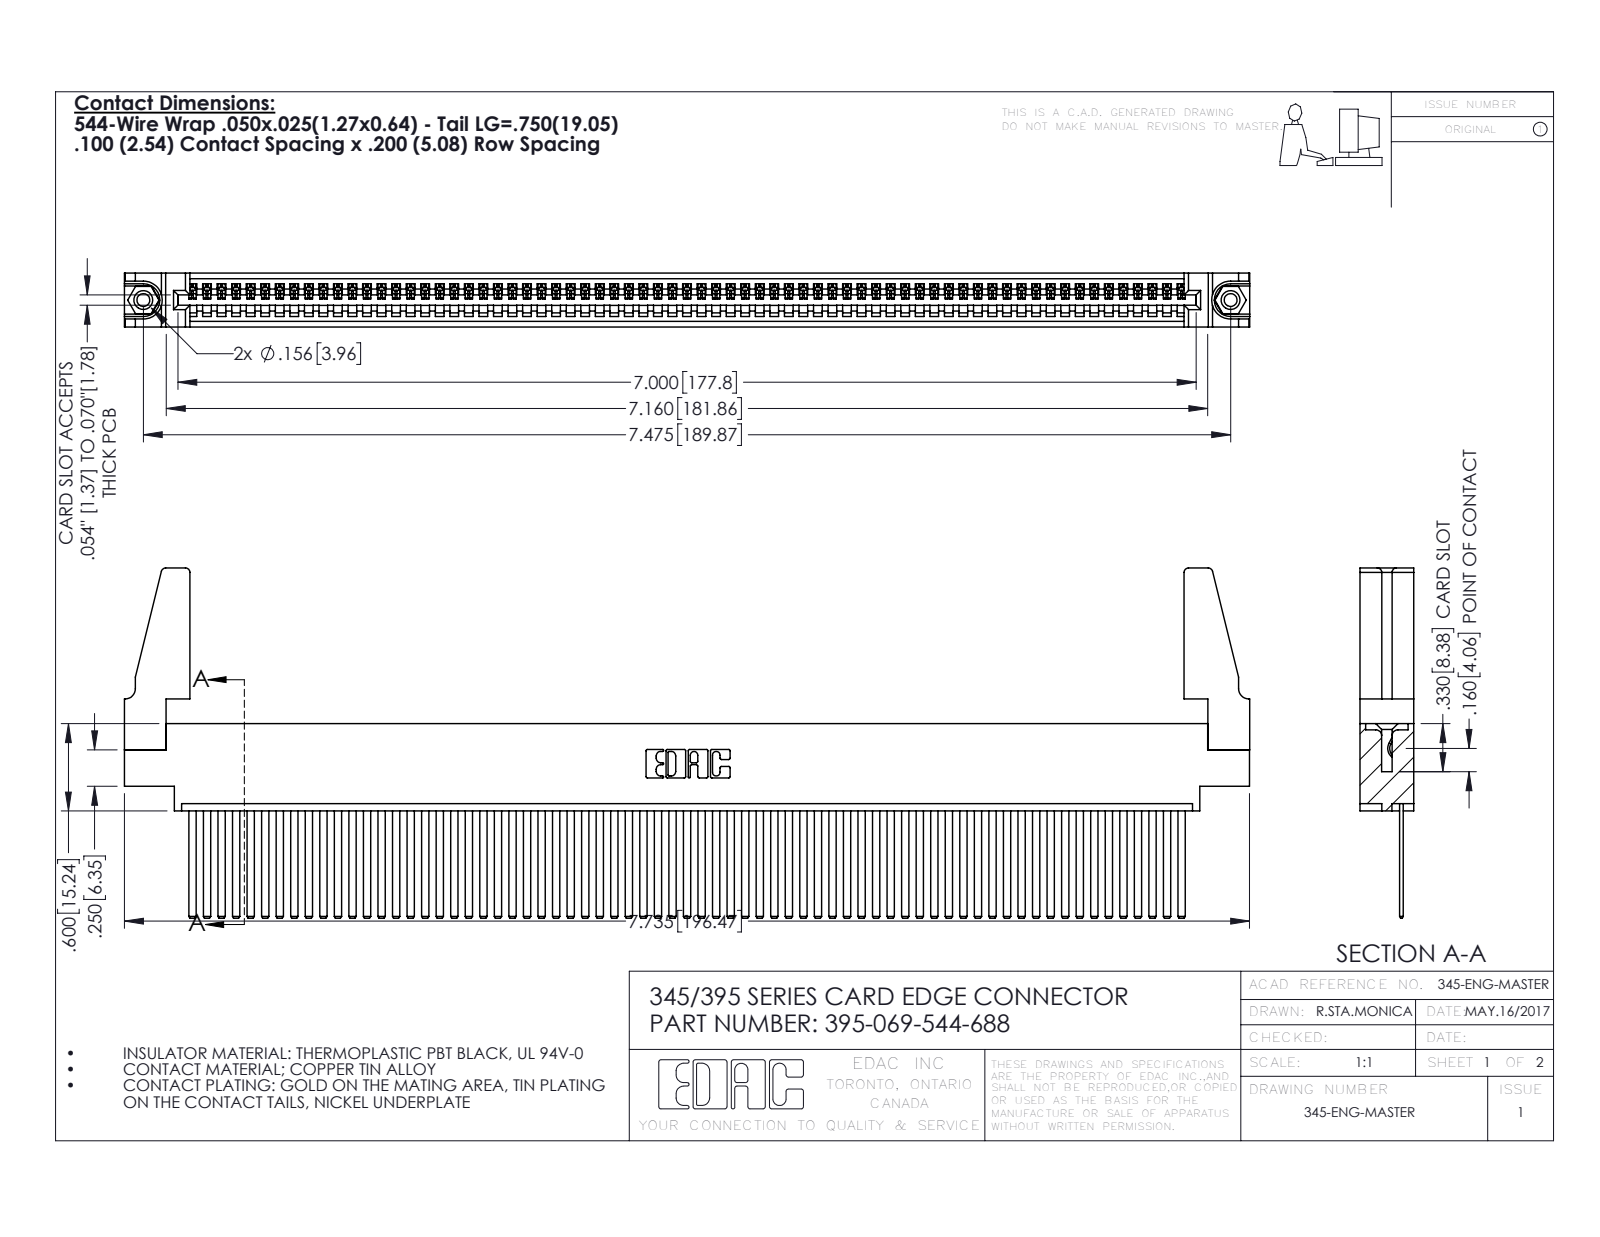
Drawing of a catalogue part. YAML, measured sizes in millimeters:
part_name: "345-250-001_345-250-001-102; 345-292-001_345-293-144; 395-069-544-688; 345-220-078_345-220-088 (+1 more)"
step_written_by: "SolidWorks 2016 (CONFIG_CONTROL_DESIGN)"
units: millimeters
bodies: {solids: 74, faces: 3842, planar: 2640, cylindrical: 1186, other: 16}
overall_size: [196.5, 61.1, 9.4]
volume: 22830
surface_area: 32030
round_holes:
  - {diameter: 2.3, count: 2}
  - {diameter: 3.2, count: 2}
  - {diameter: 4, count: 2}
  - {diameter: 1.6, count: 1}
round_bosses_or_shafts:
  - {diameter: 3.9, count: 2}
partial_cylinders:
  - {radius: 0.2, count: 138}
  - {radius: 0.3, count: 22}
  - {radius: 0.8, count: 8}
  - {radius: 0.2, count: 6}
  - {radius: 0.8, count: 6}
  - {radius: 0.7, count: 3}
  - {radius: 0.8, count: 2}
  - {radius: 1, count: 2}
face_to_face_distances: [1.8, 7.6, 2.5, 6.9, 0.6, 9.4, 5.1, 5.7, 4.4, 3.8]
hole_center_spacings: [6.9, 183.9, 189.9]
